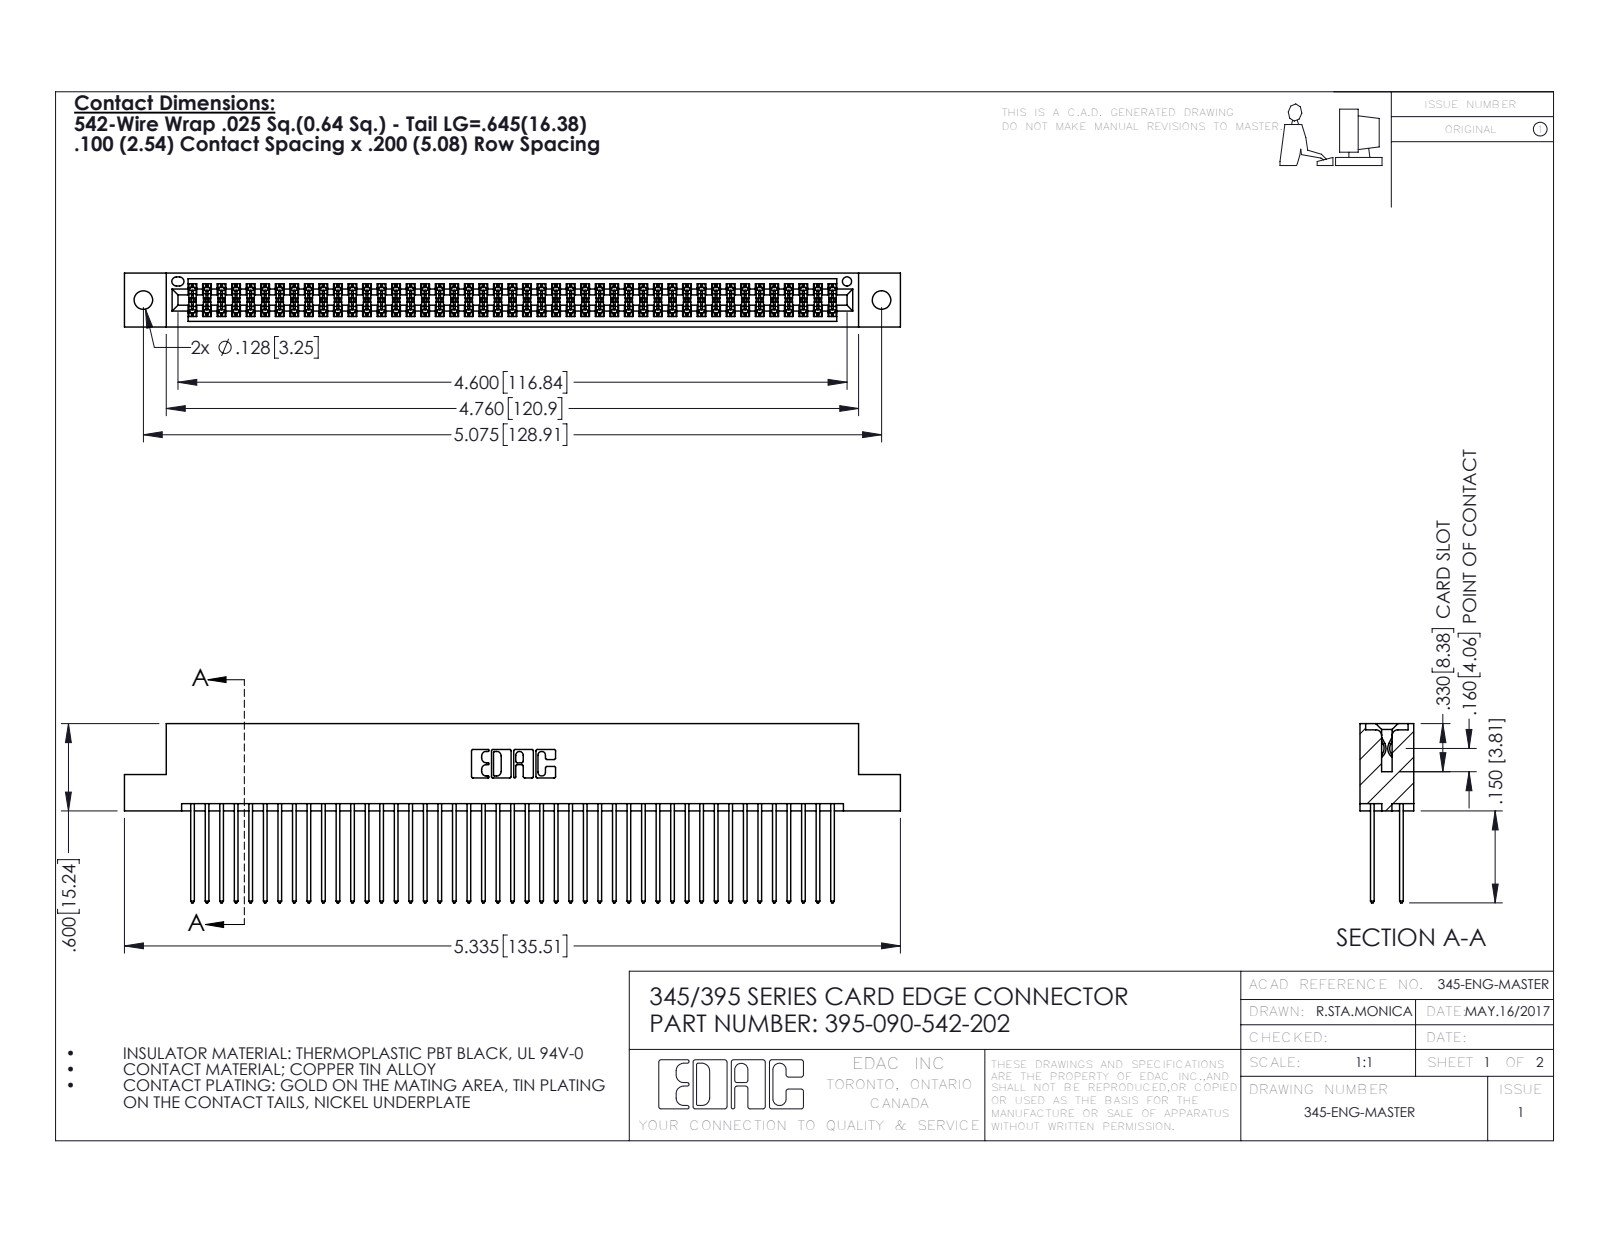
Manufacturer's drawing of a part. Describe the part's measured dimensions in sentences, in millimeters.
The part is named "345-292-001_345-293-142; 345 Part_Flush Mounting Lugs - 0.128 Dia; 395-090-542-202". Its 3-D file was written by "SolidWorks 2016 (CONFIG_CONTROL_DESIGN)". It is 91 solids with 4626 faces: 3050 planar, 1576 cylindrical and 0 other. Overall it measures 135.5 by 31.3 by 9.4 millimeters. Its volume is 13 600 cubic millimeters and its surface area 21 810 square millimeters. Round holes: 2 of diameter 3.3, 1 of diameter 1.6. Partial cylindrical surfaces (rounded edges, fillets, slot ends): 135 of radius 0.2, 90 of radius 0.3, 22 of radius 0.3, 6 of radius 0.2, 6 of radius 0.8, 3 of radius 0.7, 2 of radius 0.4, 2 of radius 0.5. The main face-to-face distances are 7.6, 1.8, 5.1, 2.5, 6.9, 0.6, 5.7, 9.4, 4.4, 3.8. The hole center spacings are 6.9, 122.9, 128.9.
